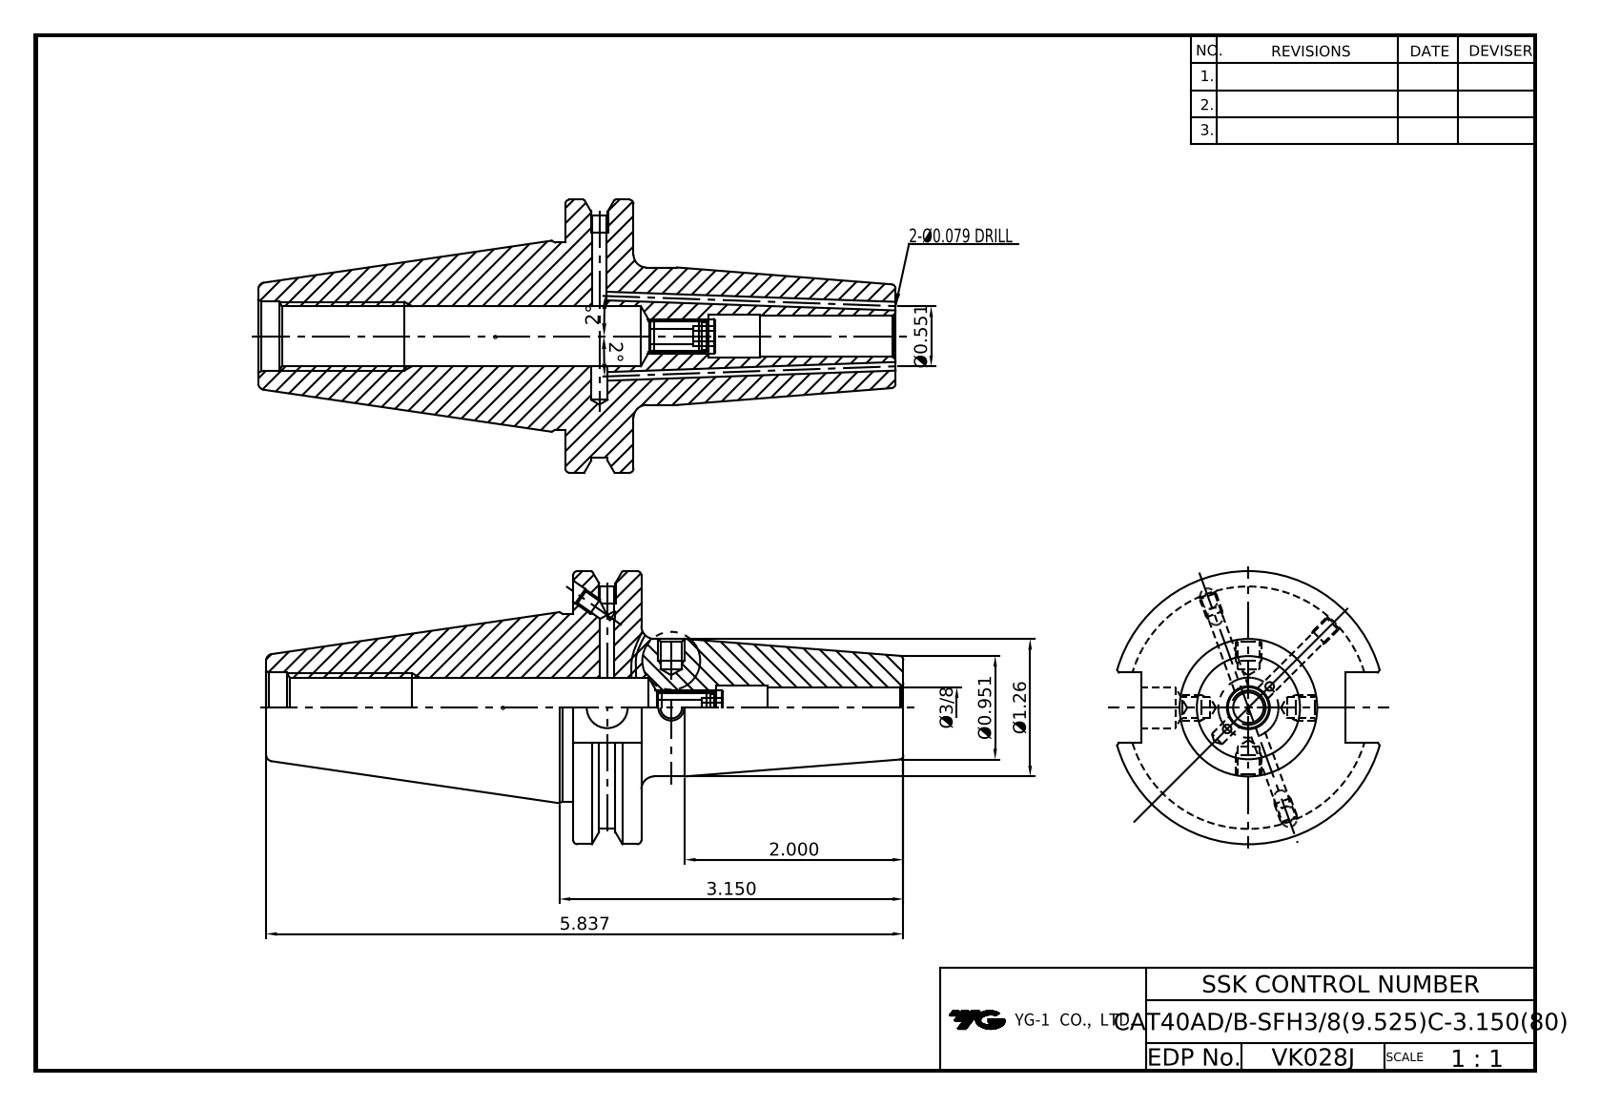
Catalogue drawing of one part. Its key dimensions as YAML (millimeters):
part_name: "LO-CAT40ADB-SFH9.525C-80"
step_written_by: "Autodesk Inventor 2024 (AUTOMOTIVE_DESIGN)"
units: millimeters
bodies: {solids: 1, faces: 92, planar: 40, cylindrical: 31, other: 21}
overall_size: [148.25, 63.5, 61.09]
volume: 136104
surface_area: 28264
round_holes:
  - {diameter: 3.24, count: 4}
  - {diameter: 2.5, count: 2}
  - {diameter: 4, count: 2}
  - {diameter: 4.2, count: 2}
  - {diameter: 9.53, count: 2}
  - {diameter: 6.92, count: 1}
  - {diameter: 10.72, count: 1}
  - {diameter: 13, count: 1}
  - {diameter: 13.39, count: 1}
  - {diameter: 16.3, count: 1}
round_bosses_or_shafts:
  - {diameter: 63.5, count: 1}
  - {diameter: 43.6, count: 1}
  - {diameter: 32, count: 1}
partial_cylinders:
  - {radius: 28.15, count: 1}
face_to_face_distances: [15.88, 76.83, 60.95, 47.6, 16.38, 71.42, 87.3, 148.25, 77.47, 6.05]
